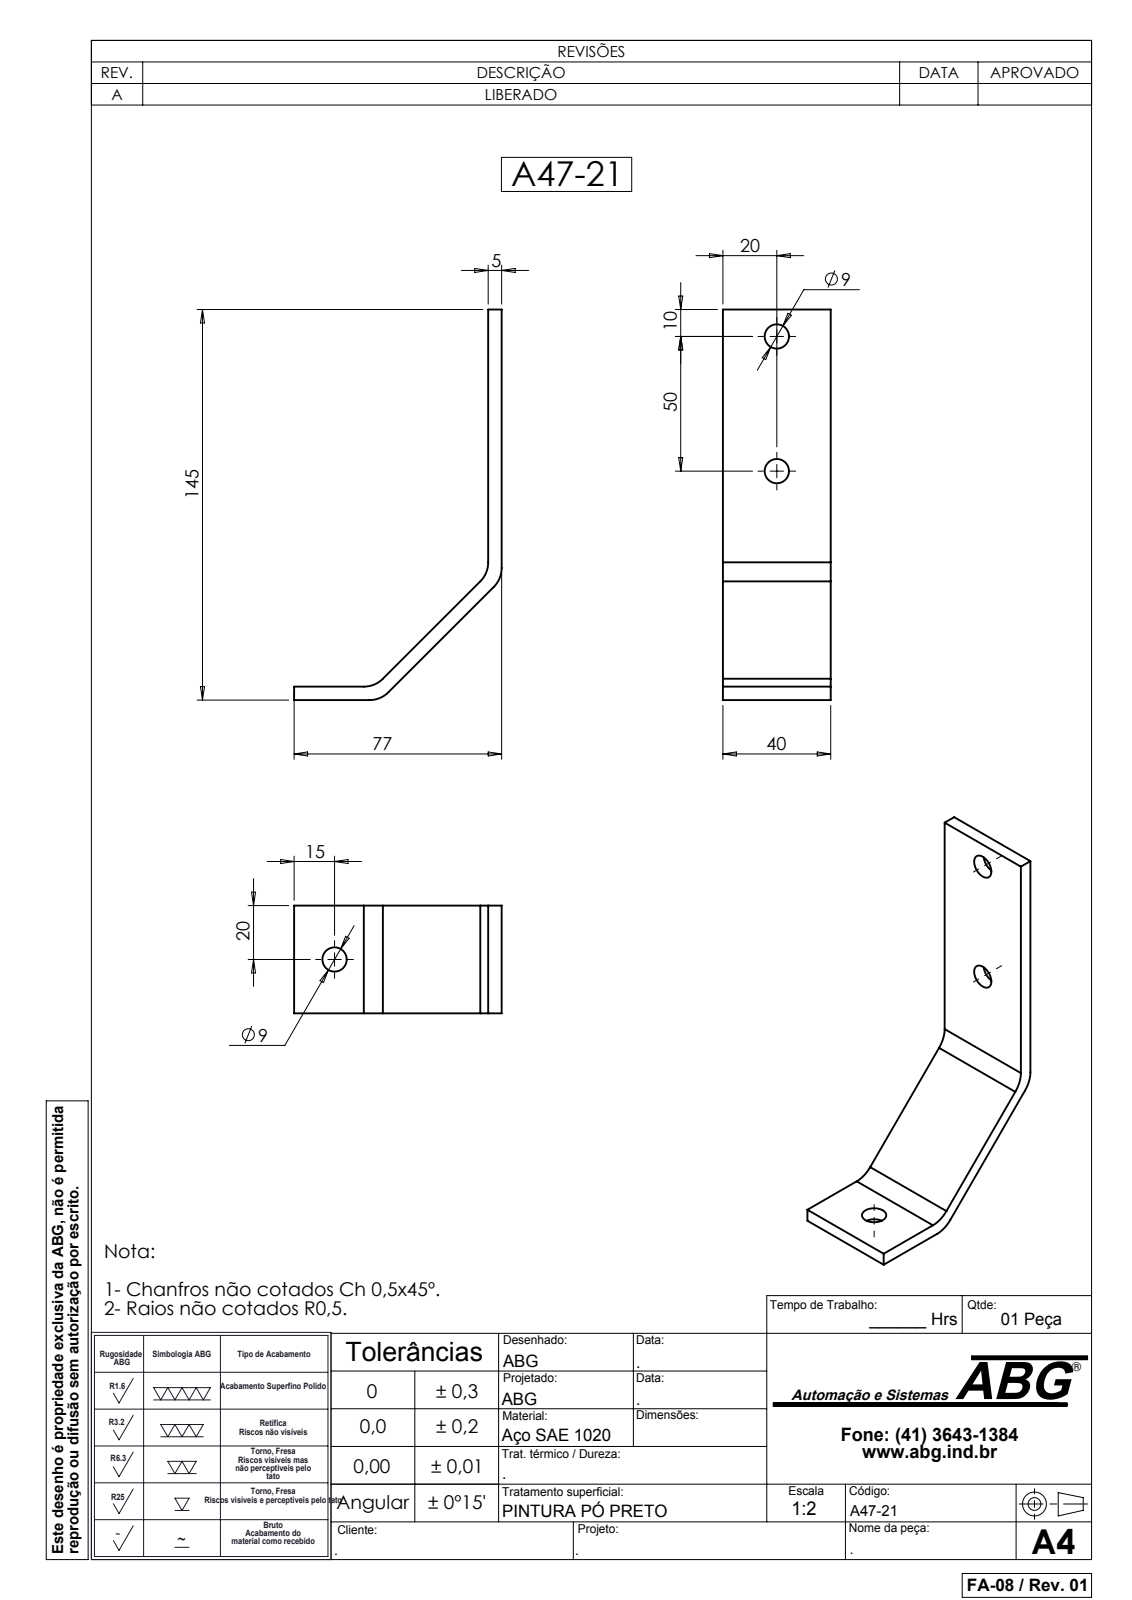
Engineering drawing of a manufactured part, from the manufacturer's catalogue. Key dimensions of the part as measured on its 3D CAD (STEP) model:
Part name (STEP PRODUCT): A47-21
STEP written by: SolidWorks 2007 (CONFIG_CONTROL_DESIGN)
Units: millimetres
Bodies: 1 solid, 20 faces (10 planar, 10 cylindrical, 0 other)
Overall size (bounding box): 145 × 77 × 40
Volume: 37 354 mm³ · Surface area: 17 612 mm²
Round holes (diameter × count): ⌀9 ×3
Partial cylindrical surfaces — rounded edges, fillets, slot ends (radius × count): R10 ×4
Main face-to-face distances: 5, 40, 145, 140, 77, 72
Hole centre spacings: 50
